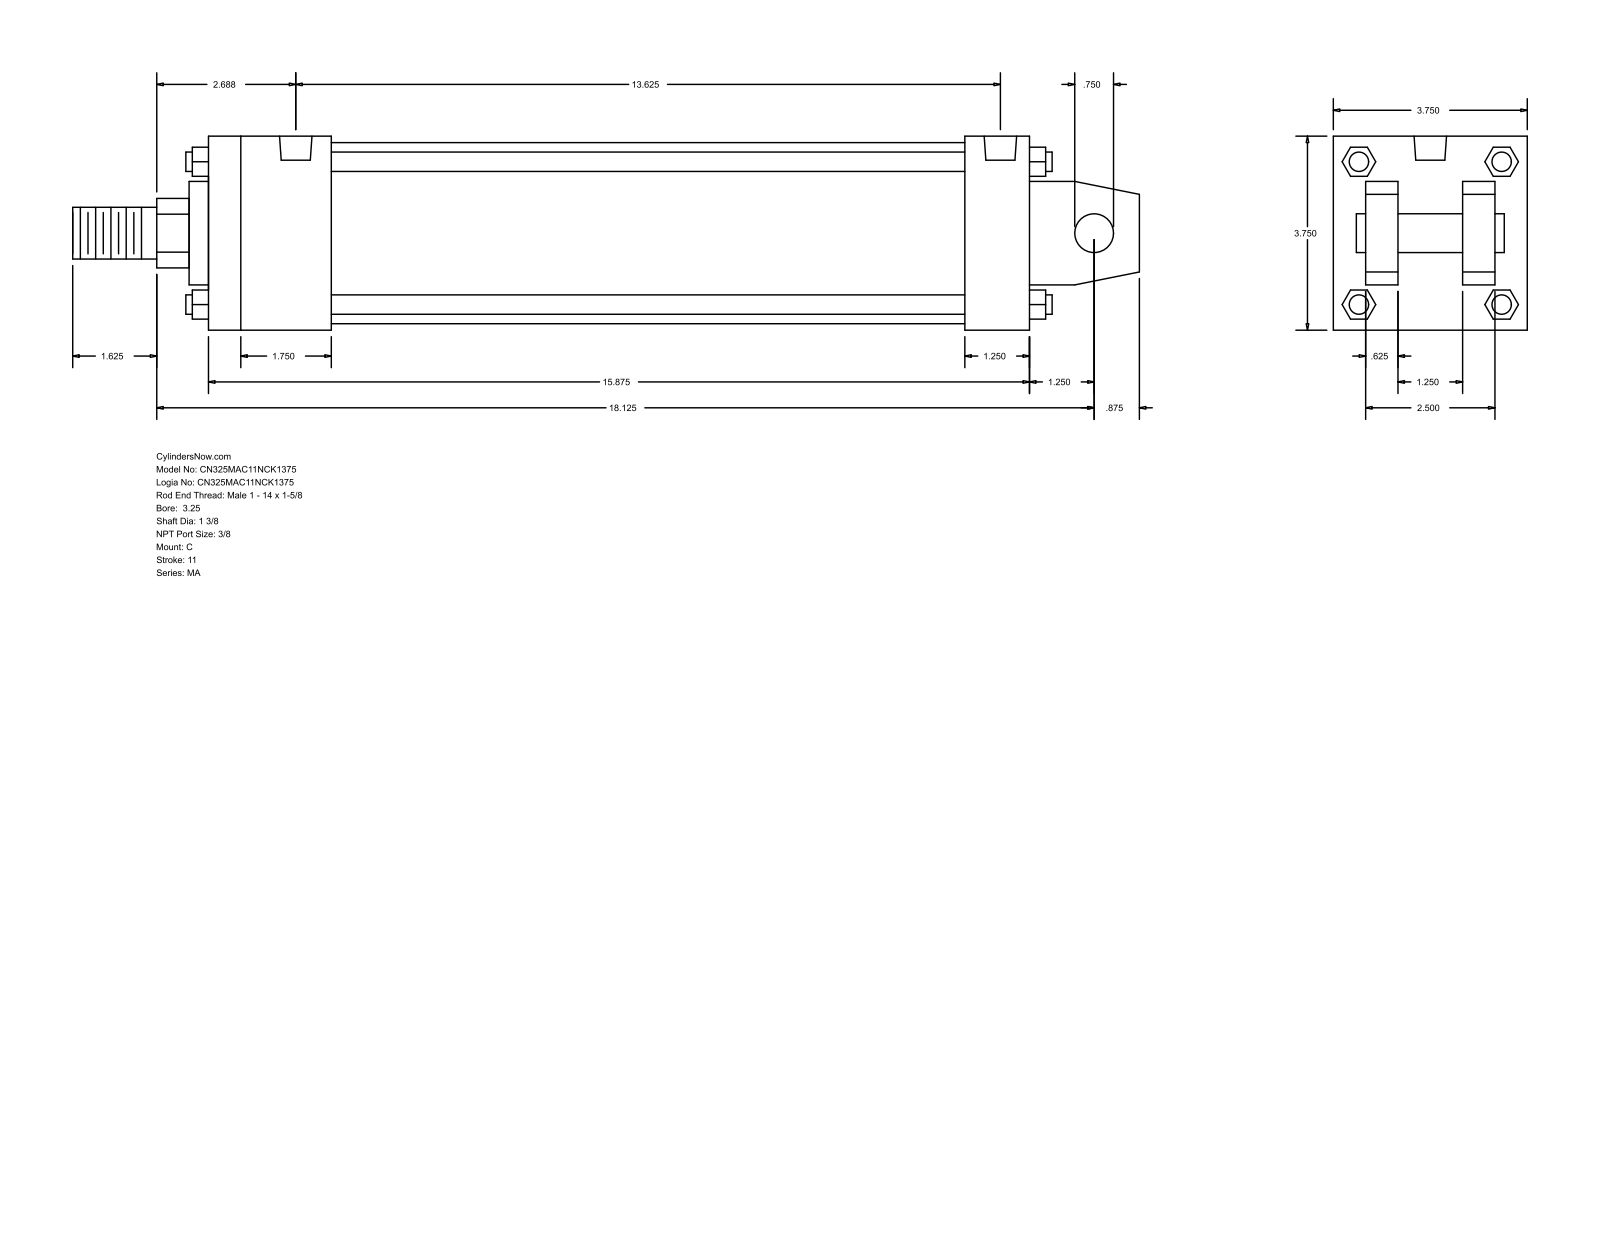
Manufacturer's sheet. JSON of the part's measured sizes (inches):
{"part_name": "MA_C__0325_1.375", "step_written_by": "GSSL Pune (CONFIG_CONTROL_DESIGN)", "units": "inches", "bodies": {"solids": 0, "faces": 139, "planar": 108, "cylindrical": 31, "other": 0}, "overall_size": [20.625, 3.75, 3.75], "round_holes": [[0.437, 4], [0.627, 2]], "round_bosses_or_shafts": [[0.375, 4], [3.5, 1], [2, 1], [1.375, 1], [1, 1], [0.75, 1]], "partial_cylinders_radius": [[0.672, 1]], "face_to_face_distances": [3.75, 0.625, 1.25, 2.5, 15.875, 3.125, 1.875, 14.625, 2.375, 12.25], "hole_center_spacings": [0.188, 13.25, 13.437, 13.625]}
